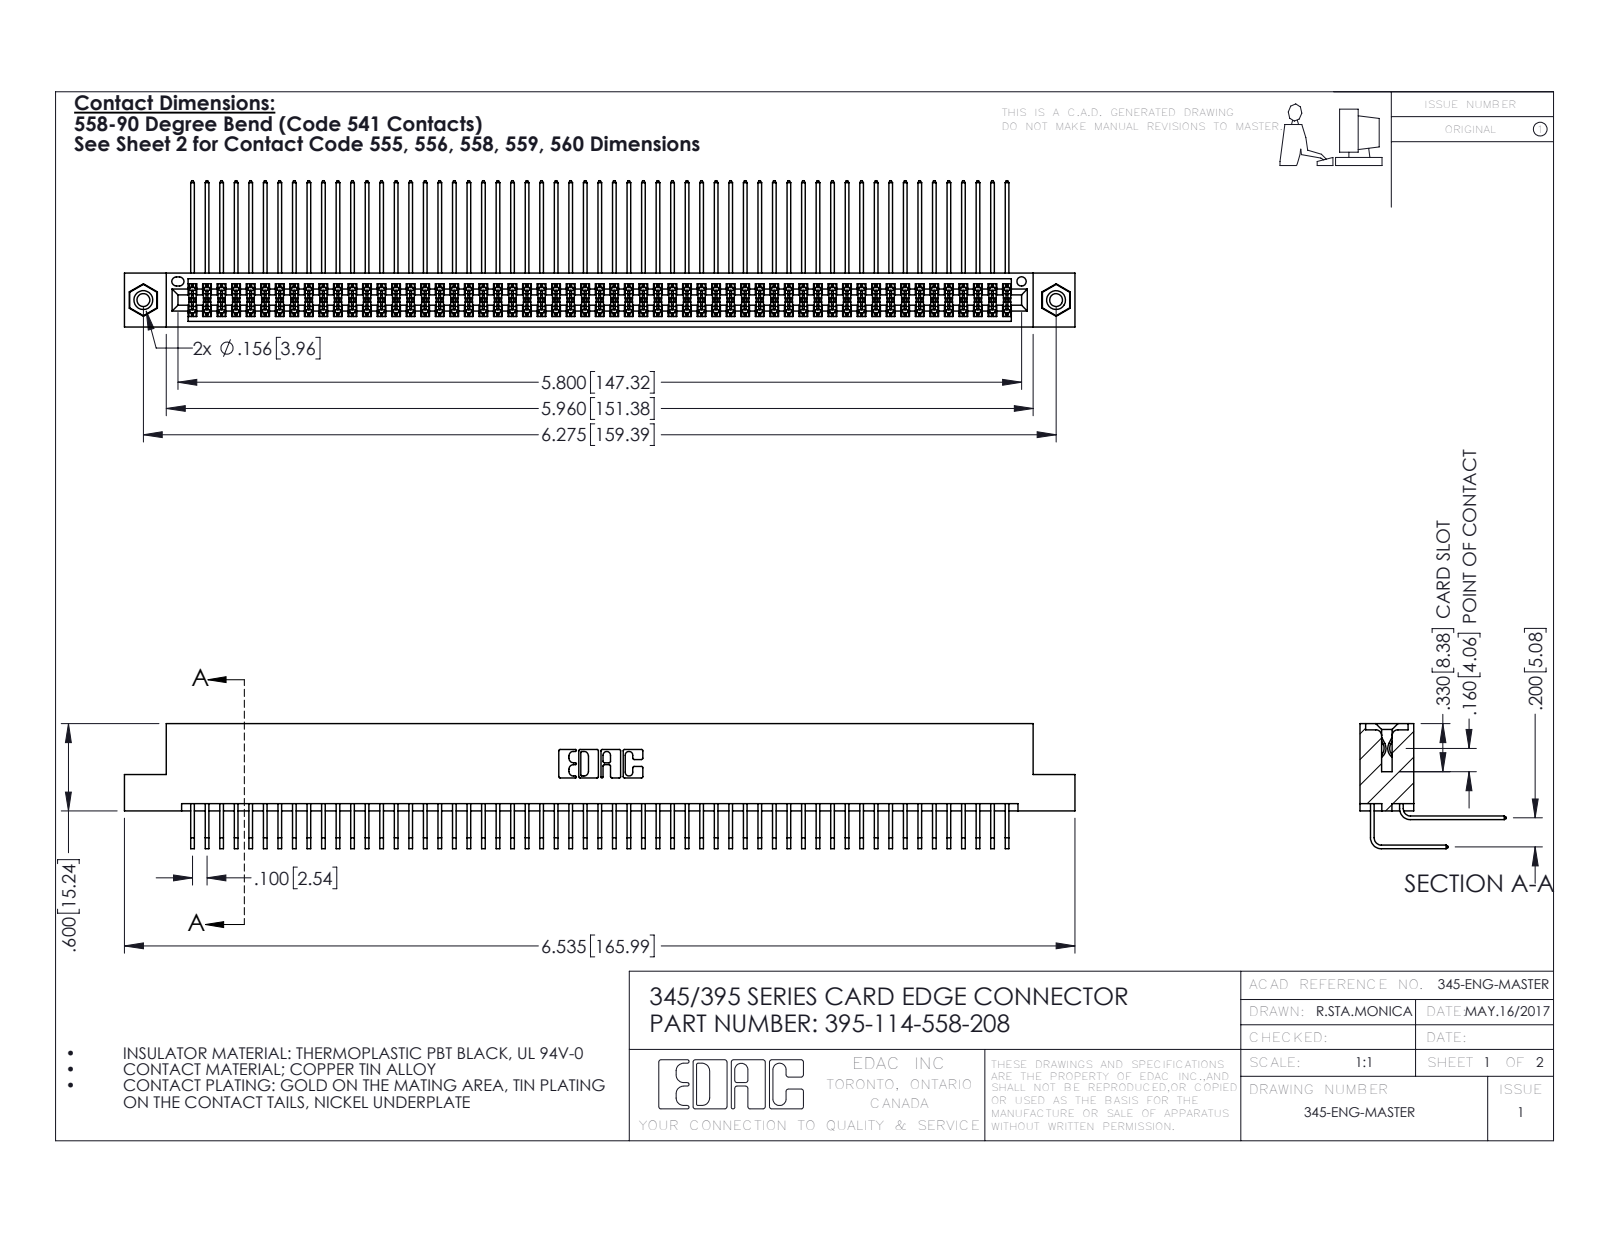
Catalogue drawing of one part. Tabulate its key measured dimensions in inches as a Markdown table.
| quantity | value |
| --- | --- |
| part name | 345 Part_Flush Mounting Lugs - 0.156 Dia-TI; 395-114-558-208; 345-292-001_558 559 Tail - 1; 345-292-001_558 Tail - 2 (+1 more) |
| STEP written by | SolidWorks 2016 (CONFIG_CONTROL_DESIGN) |
| units | inches |
| bodies | 117 solids, 6114 faces (4102 planar, 1996 cylindrical, 16 other) |
| overall size | 6.535 × 1.005 × 0.859 |
| volume | 1.032 in³ |
| surface area | 44.02 in² |
| round holes (diameter × count) | 0.089 × 2, 0.125 × 2, 0.156 × 2, 0.064 × 1 |
| round bosses / shafts (diameter × count) | 0.155 × 2 |
| partial cylindrical surfaces (radius × count) | 0.006 × 172, 0.01 × 22, 0.007 × 6, 0.031 × 6, 0.026 × 3, 0.014 × 2, 0.019 × 2, 0.022 × 2 |
| main face-to-face distances | 0.072, 0.298, 0.2, 0.37, 0.098, 0.272, 0.025, 0.225, 0.025, 0.175 |
| hole center spacings | 0.27, 6.039, 6.275 |
